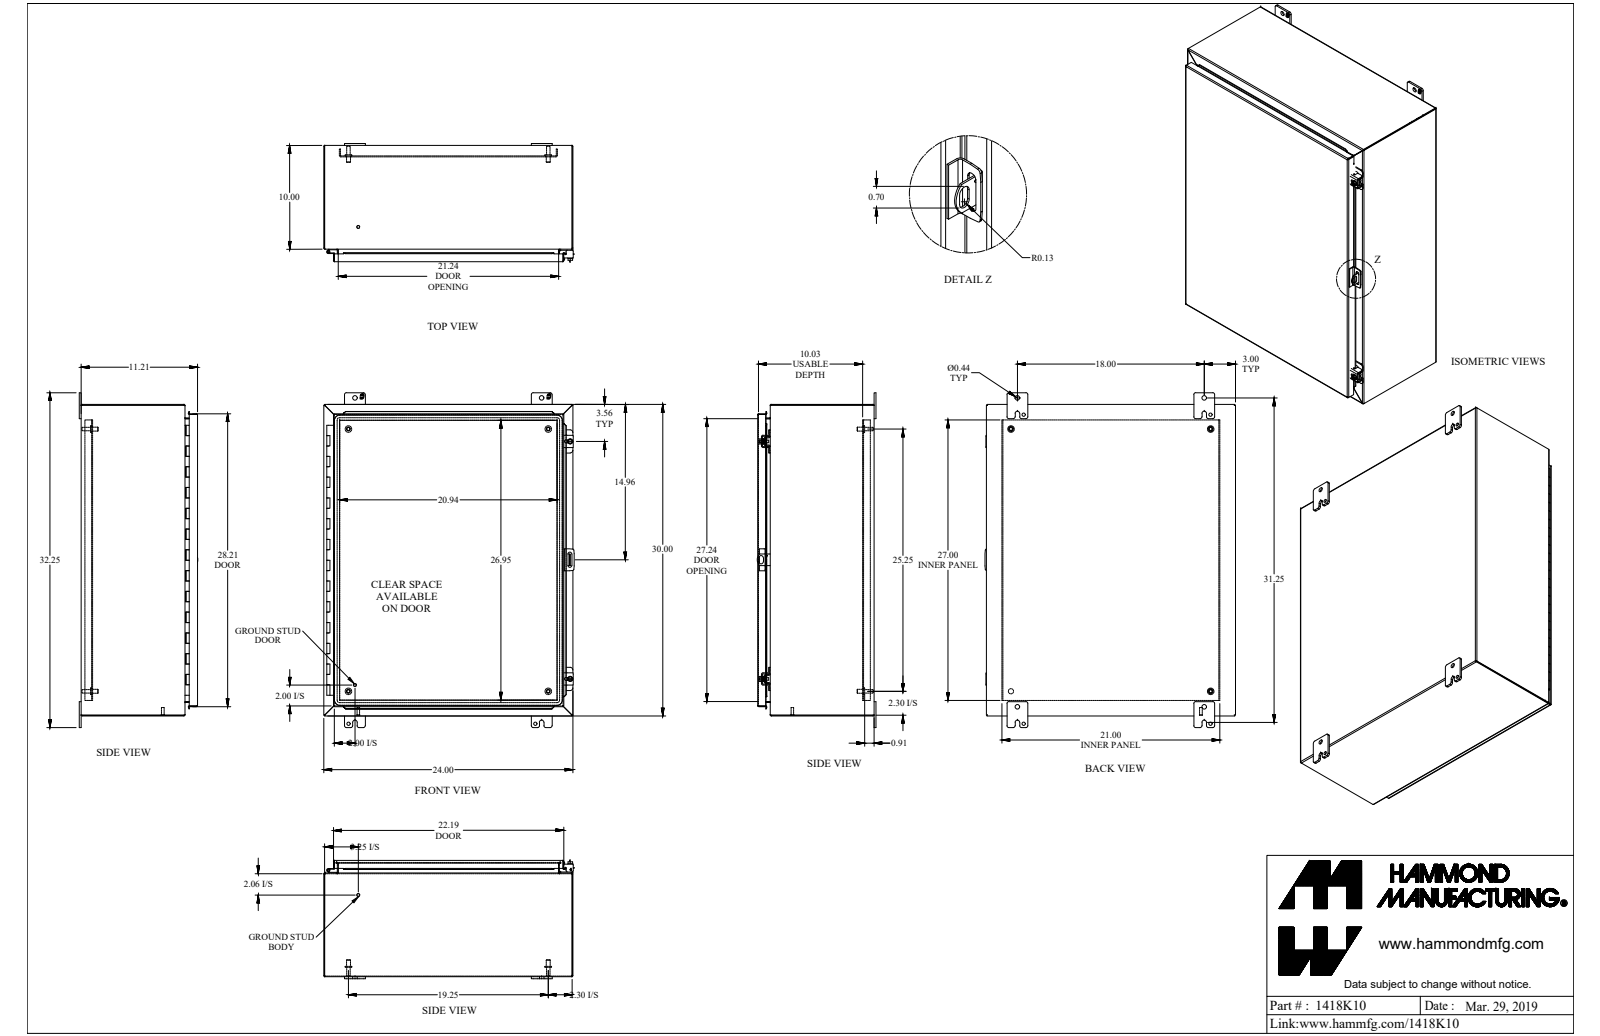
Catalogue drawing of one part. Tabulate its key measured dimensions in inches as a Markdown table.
| quantity | value |
| --- | --- |
| part name | 1418K10_Default |
| STEP written by | SolidWorks 2019 (CONFIG_CONTROL_DESIGN) |
| units | inches |
| bodies | 38 solids, 1207 faces (739 planar, 400 cylindrical, 68 other) |
| overall size | 32.25 × 24.125 × 11.437 |
| volume | 279 in³ |
| surface area | 7 248 in² |
| round holes (diameter × count) | 0.313 × 4, 0.437 × 4, 0.5 × 4, 0.213 × 2, 0.265 × 2, 0.307 × 2, 0.375 × 2, 0.445 × 2, 0.125 × 1, 0.187 × 1 |
| round bosses / shafts (diameter × count) | 0.65 × 4, 0.375 × 4, 0.33 × 4, 1 × 2, 0.5 × 2, 0.39 × 2, 0.281 × 2, 0.25 × 2 |
| partial cylindrical surfaces (radius × count) | 0.188 × 26, 0.036 × 24, 0.108 × 24, 0.048 × 13, 0.143 × 13, 0.045 × 8, 0.218 × 8, 0.25 × 8 |
| main face-to-face distances | 0.072, 11.113, 11.041, 11.185, 0.937, 0.095, 1.009, 23.928, 10.081, 10.009 |
| hole center spacings | 31.751, 1.735, 18, 19.25, 29.75, 31.751, 34.772, 2.434 |
